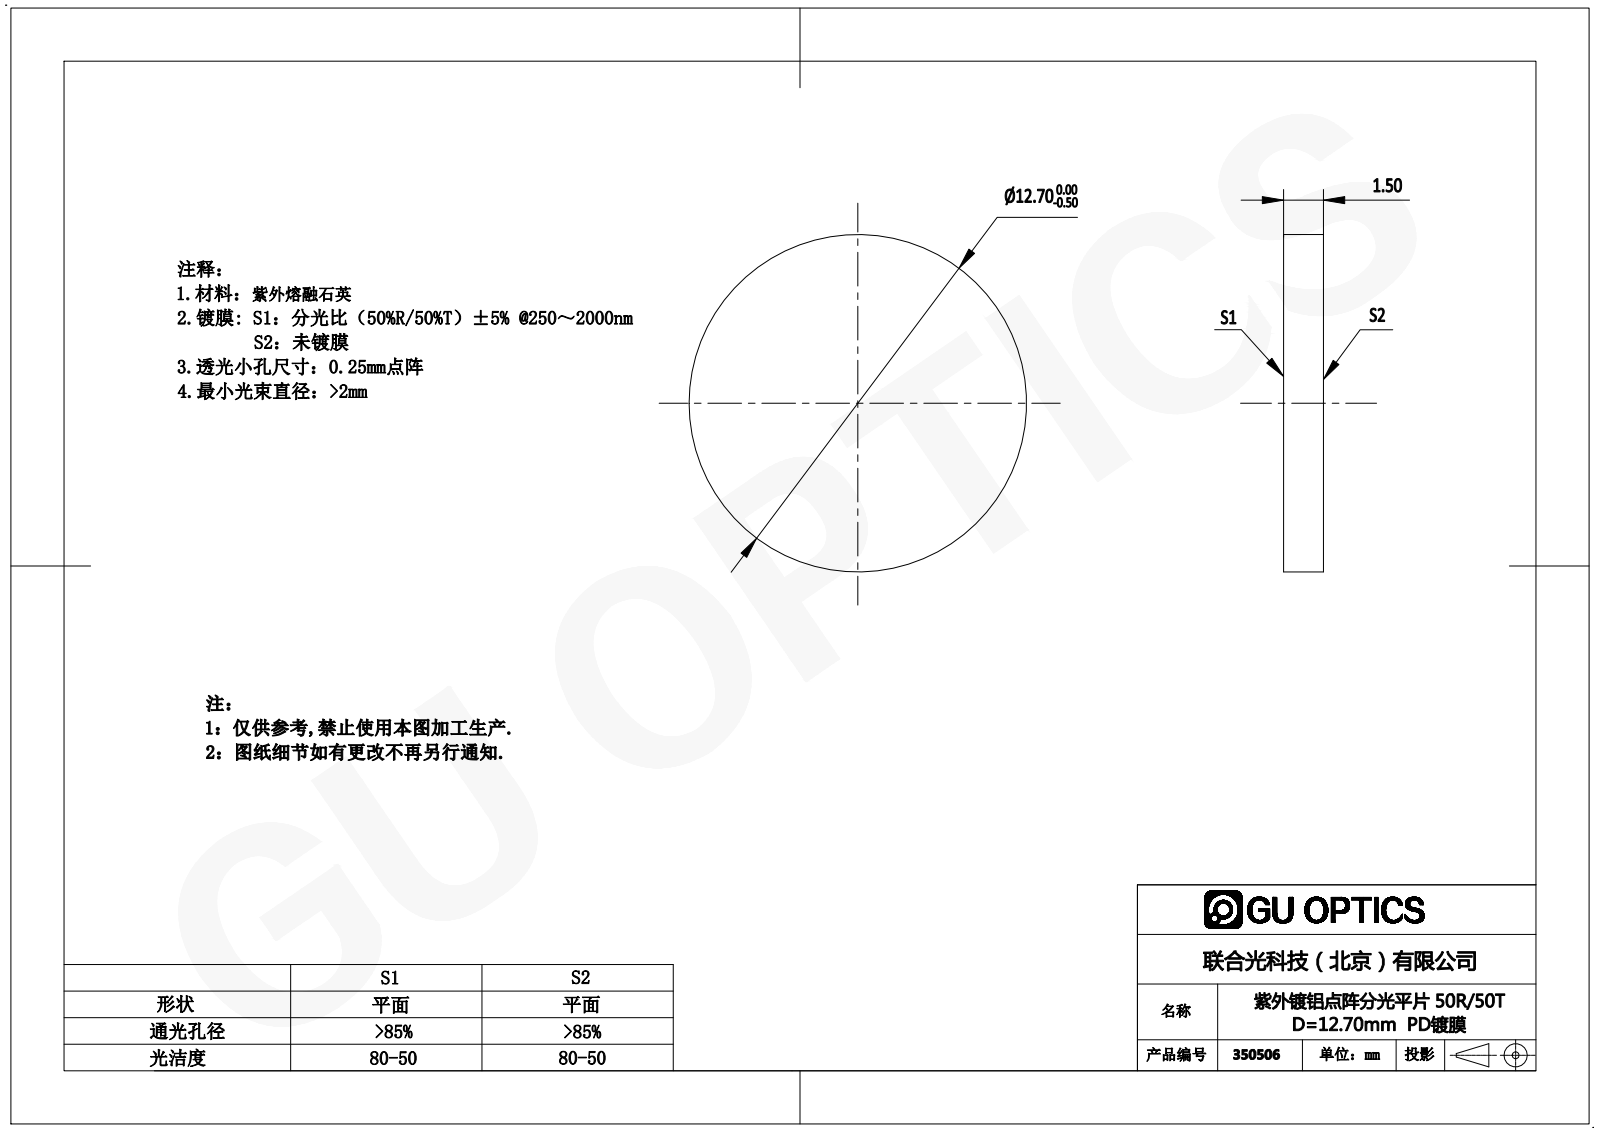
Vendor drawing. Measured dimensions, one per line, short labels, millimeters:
name: 350500
written by: SolidWorks 2016 (AUTOMOTIVE_DESIGN)
unit: mm
bodies: 1 solid, 4 faces (2 planar, 2 cylindrical, 0 other)
size: 12.7 × 12.7 × 1.5
volume: 190 mm³; area: 313 mm²
bosses: 1× ⌀12.7
face distances: 1.5
